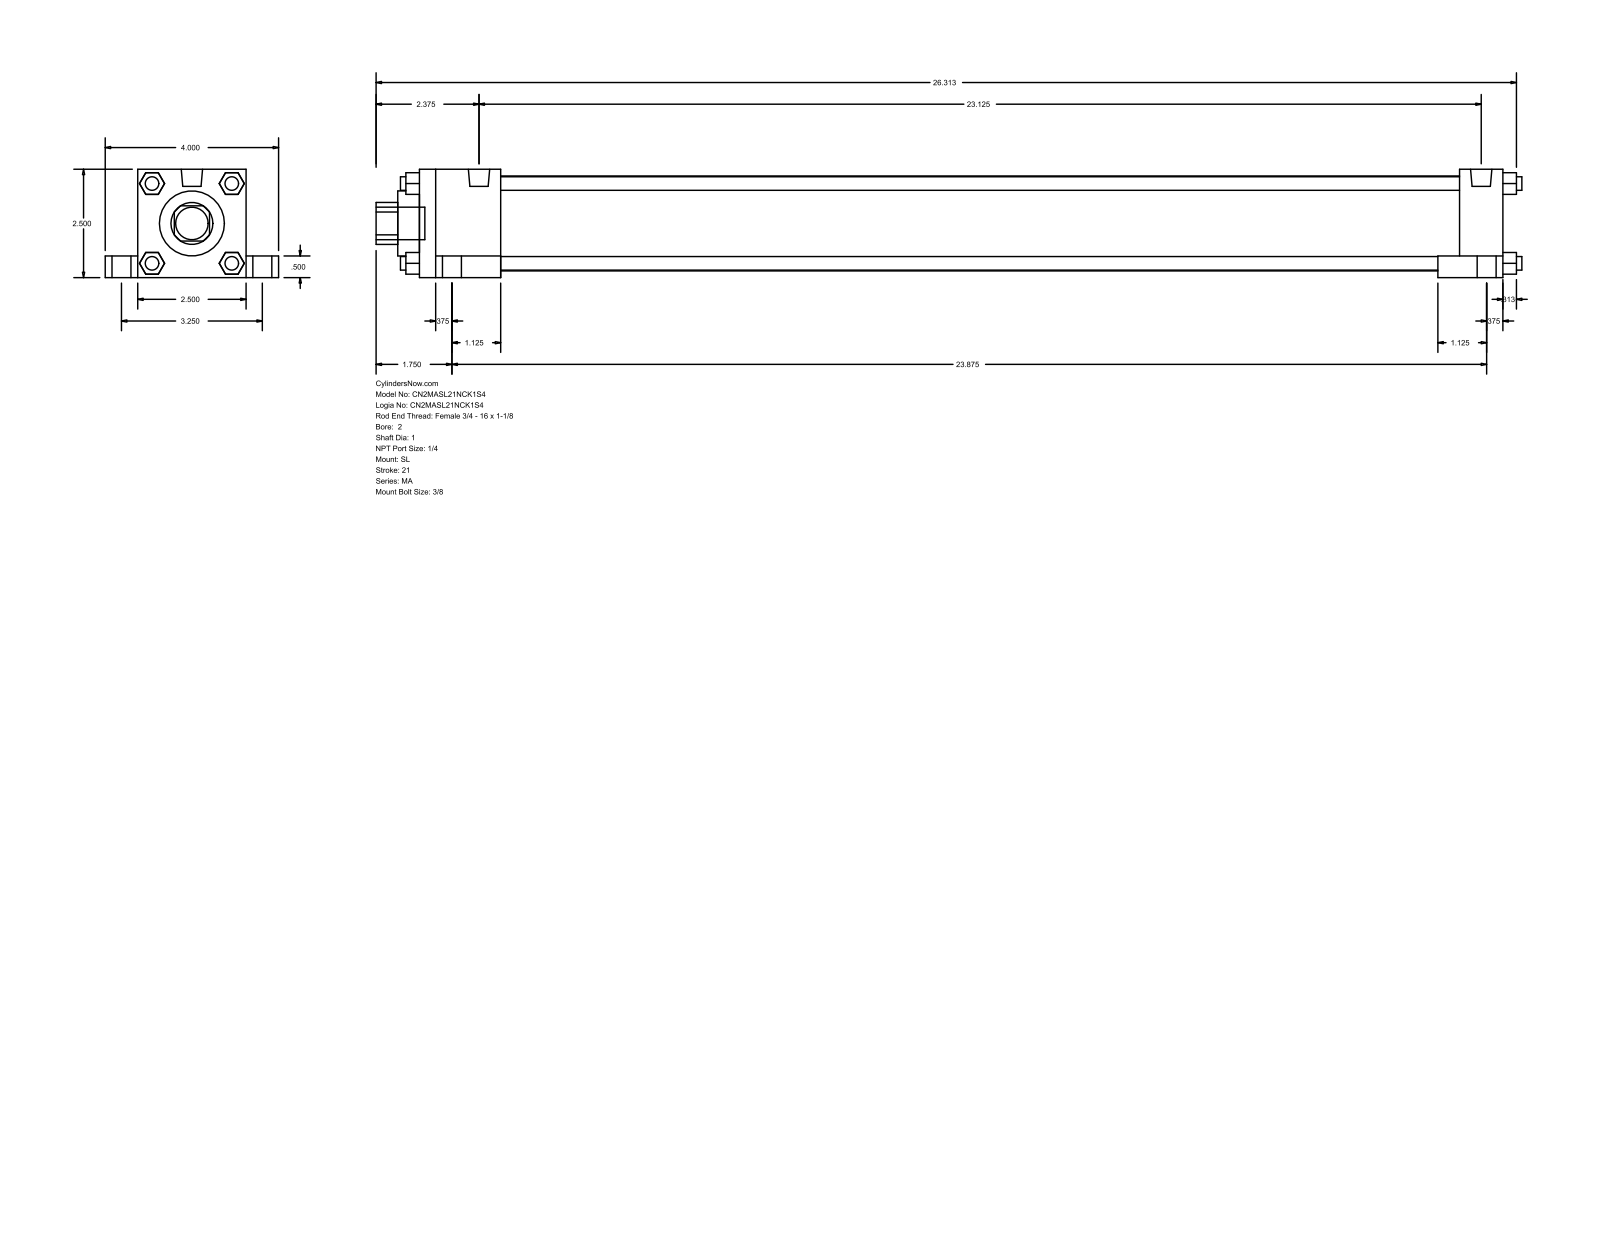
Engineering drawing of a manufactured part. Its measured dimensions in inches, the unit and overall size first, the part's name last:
Units: inches
Overall size (bounding box): 26.437 × 4 × 2.5
Round holes (diameter × count): ⌀1 ×1, ⌀1.5 ×1, ⌀2.19 ×1
Round bosses / shafts (diameter × count): ⌀0.313 ×8, ⌀0.687 ×4, ⌀0.437 ×4, ⌀0.492 ×2, ⌀0.75 ×1
Partial cylindrical surfaces — rounded edges, fillets, slot ends (radius × count): R0.484 ×1
Main face-to-face distances: 2.5, 0.5, 25, 0.75, 3.25, 1, 2, 1.875, 23.125, 24
Bodies: 0 solids, 148 faces (112 planar, 36 cylindrical, 0 other)
Part name (STEP PRODUCT): MA_SL__0200_1
STEP written by: GSSL Pune (CONFIG_CONTROL_DESIGN)
